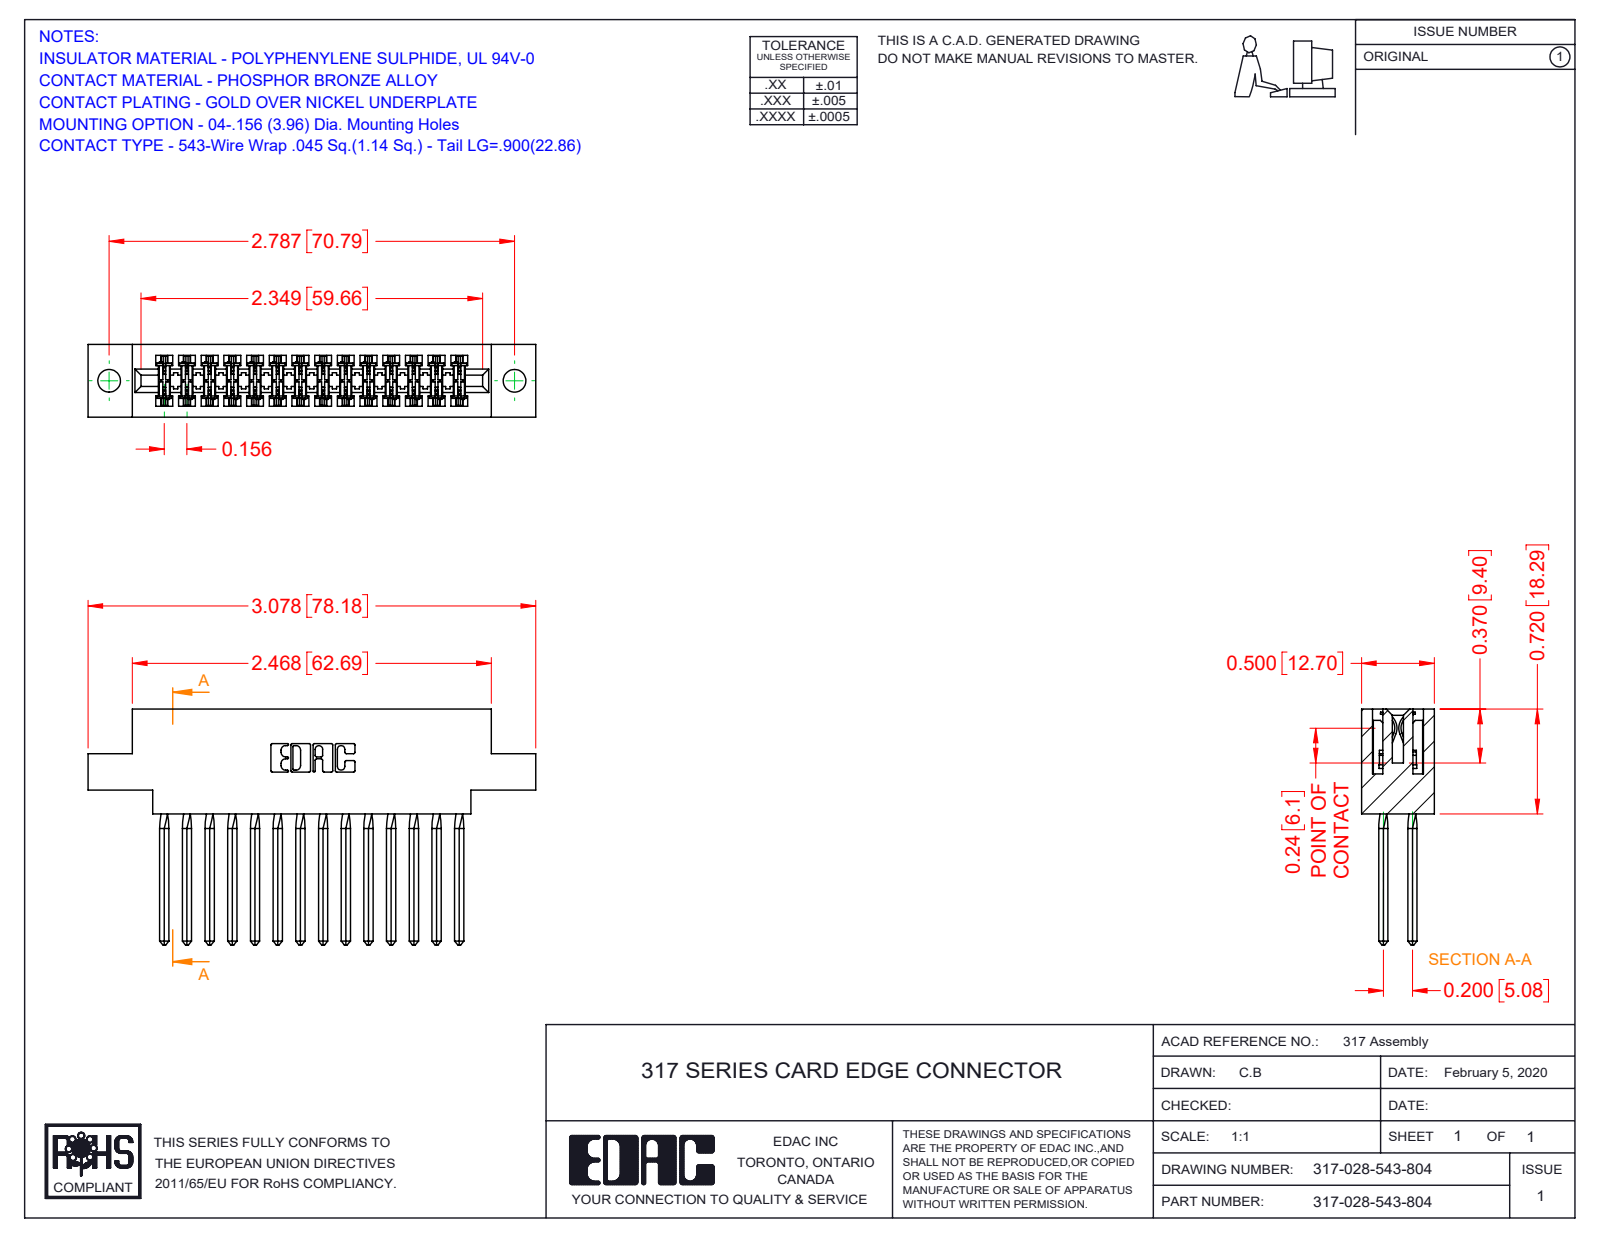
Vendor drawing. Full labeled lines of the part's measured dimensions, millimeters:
Part name (STEP PRODUCT): 317-028-543-804; 317 Part_.156 Dia - TH; 317-290-001_543
STEP written by: SolidWorks 2016 (CONFIG_CONTROL_DESIGN)
Units: millimetres
Bodies: 29 solids, 2594 faces (2102 planar, 380 cylindrical, 112 other)
Overall size (bounding box): 78.2 × 41.1 × 12.7
Volume: 12 200 mm³ · Surface area: 17 280 mm²
Round holes (diameter × count): ⌀4 ×2
Partial cylindrical surfaces — rounded edges, fillets, slot ends (radius × count): R0.4 ×56, R0.3 ×22, R0.2 ×6, R0.8 ×6, R0.7 ×3, R2.4 ×2, R2.5 ×2, R2.8 ×2
Main face-to-face distances: 12.7, 1.9, 10.8, 2.8, 5.6, 8.9, 8.4, 2.9, 18.3, 5
Hole centre spacings: 70.8
